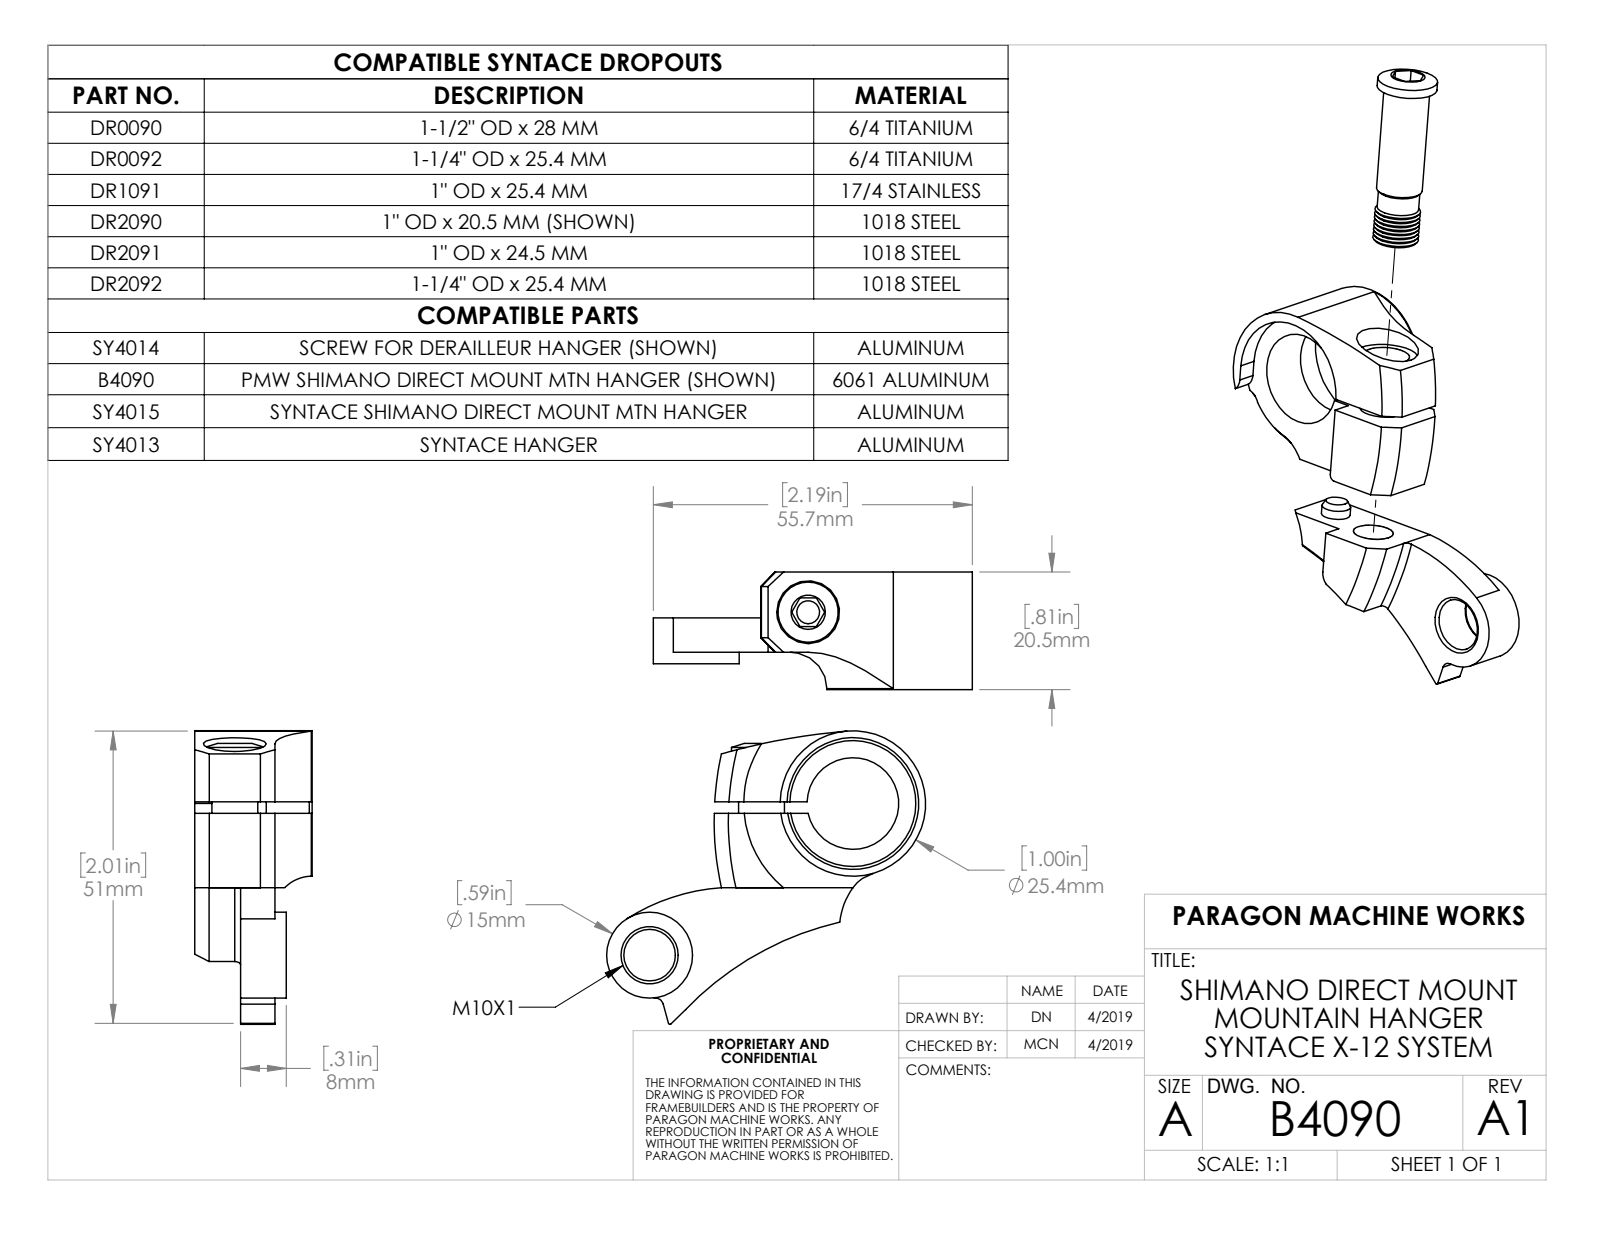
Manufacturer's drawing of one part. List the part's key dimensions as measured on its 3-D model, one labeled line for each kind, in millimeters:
Part name (STEP PRODUCT): DR4090
STEP written by: SolidWorks 2014 (AUTOMOTIVE_DESIGN)
Units: millimetres
Bodies: 1 solid, 38 faces (10 planar, 15 cylindrical, 13 other)
Overall size (bounding box): 42.99 × 26.34 × 16
Volume: 3 931 mm³ · Surface area: 2 501 mm²
Round holes (diameter × count): ⌀7 ×1, ⌀9 ×1
Round bosses / shafts (diameter × count): ⌀15 ×1, ⌀5 ×1
Partial cylindrical surfaces — rounded edges, fillets, slot ends (radius × count): R0.25 ×1, R1.5 ×1, R2.5 ×1, R13 ×1, R35.52 ×1, R54.2 ×1, R63.91 ×1
Main face-to-face distances: 6, 8, 2, 14, 16, 3.5, 4.5, 10.5, 12.5, 2.5
